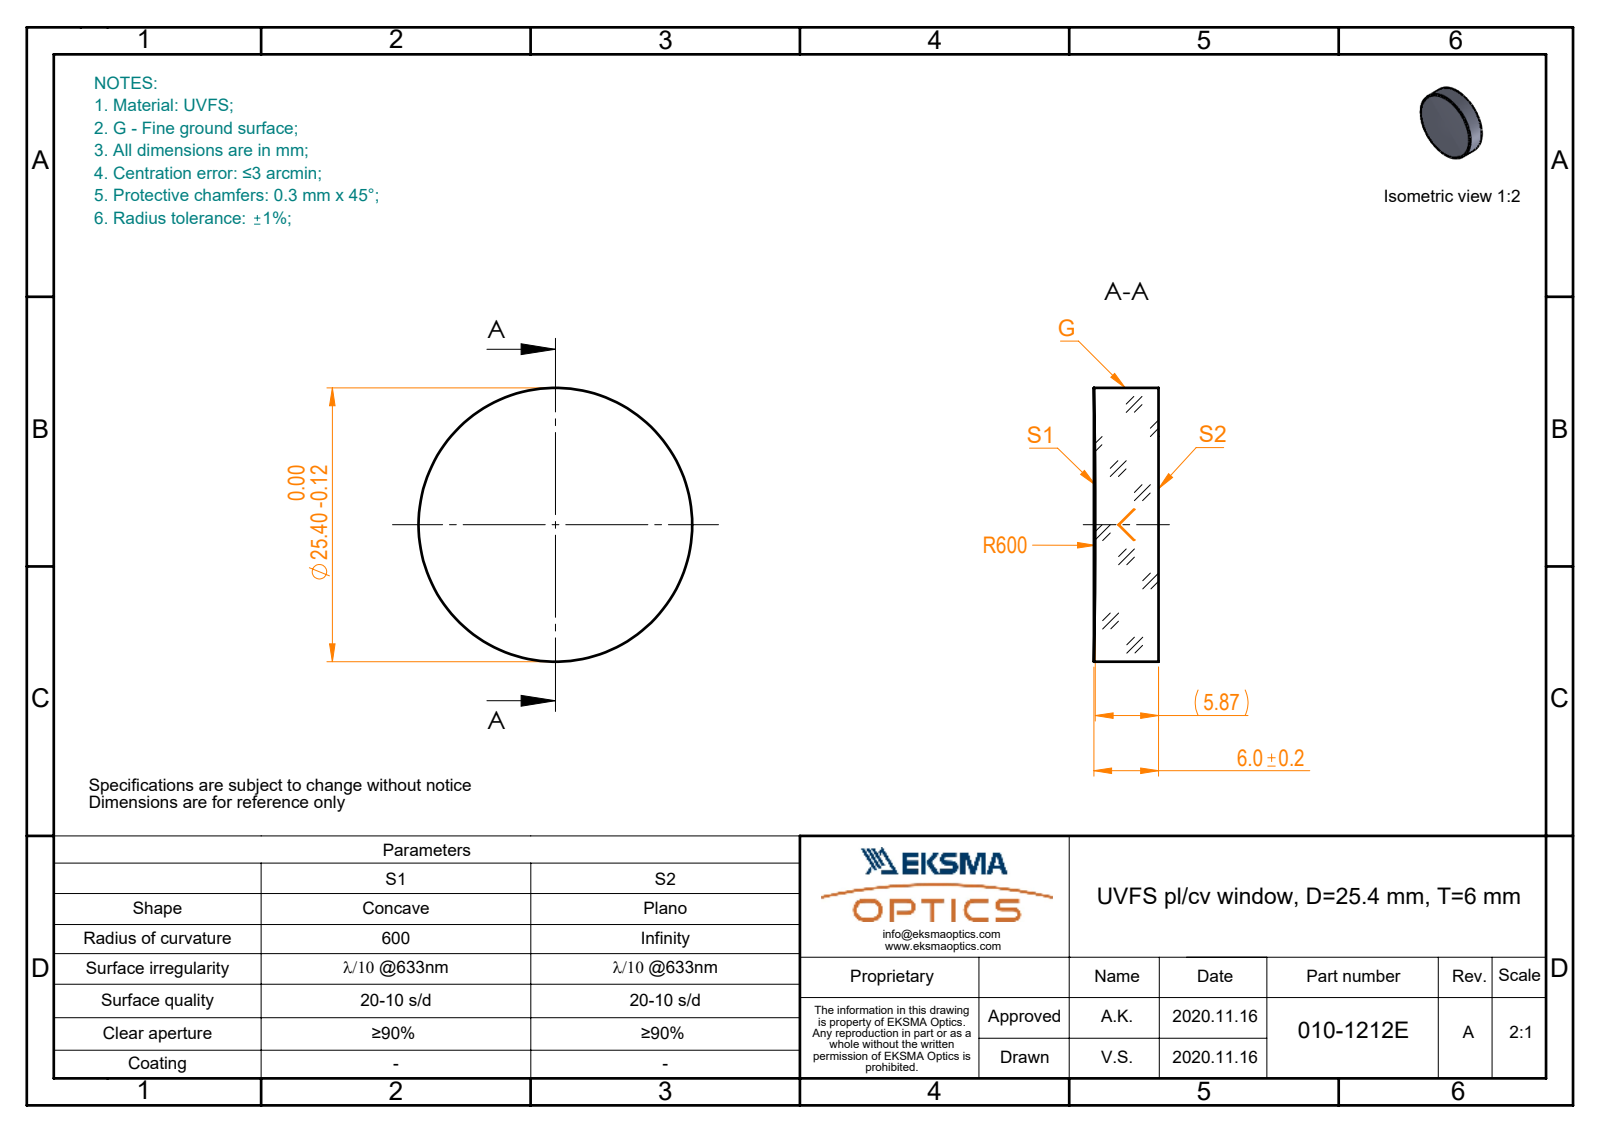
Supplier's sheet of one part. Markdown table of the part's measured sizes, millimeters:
| quantity | value |
| --- | --- |
| part name | 010-1212E_UVFS_PCV_window |
| STEP written by | SolidWorks 2019 (CONFIG_CONTROL_DESIGN) |
| units | millimeters |
| bodies | 1 solid, 5 faces (1 planar, 2 cylindrical, 2 other) |
| overall size | 25.4 × 25.4 × 6 |
| volume | 3 006 mm³ |
| surface area | 1 492 mm² |
| round bosses / shafts (diameter × count) | 25.4 × 1 |
